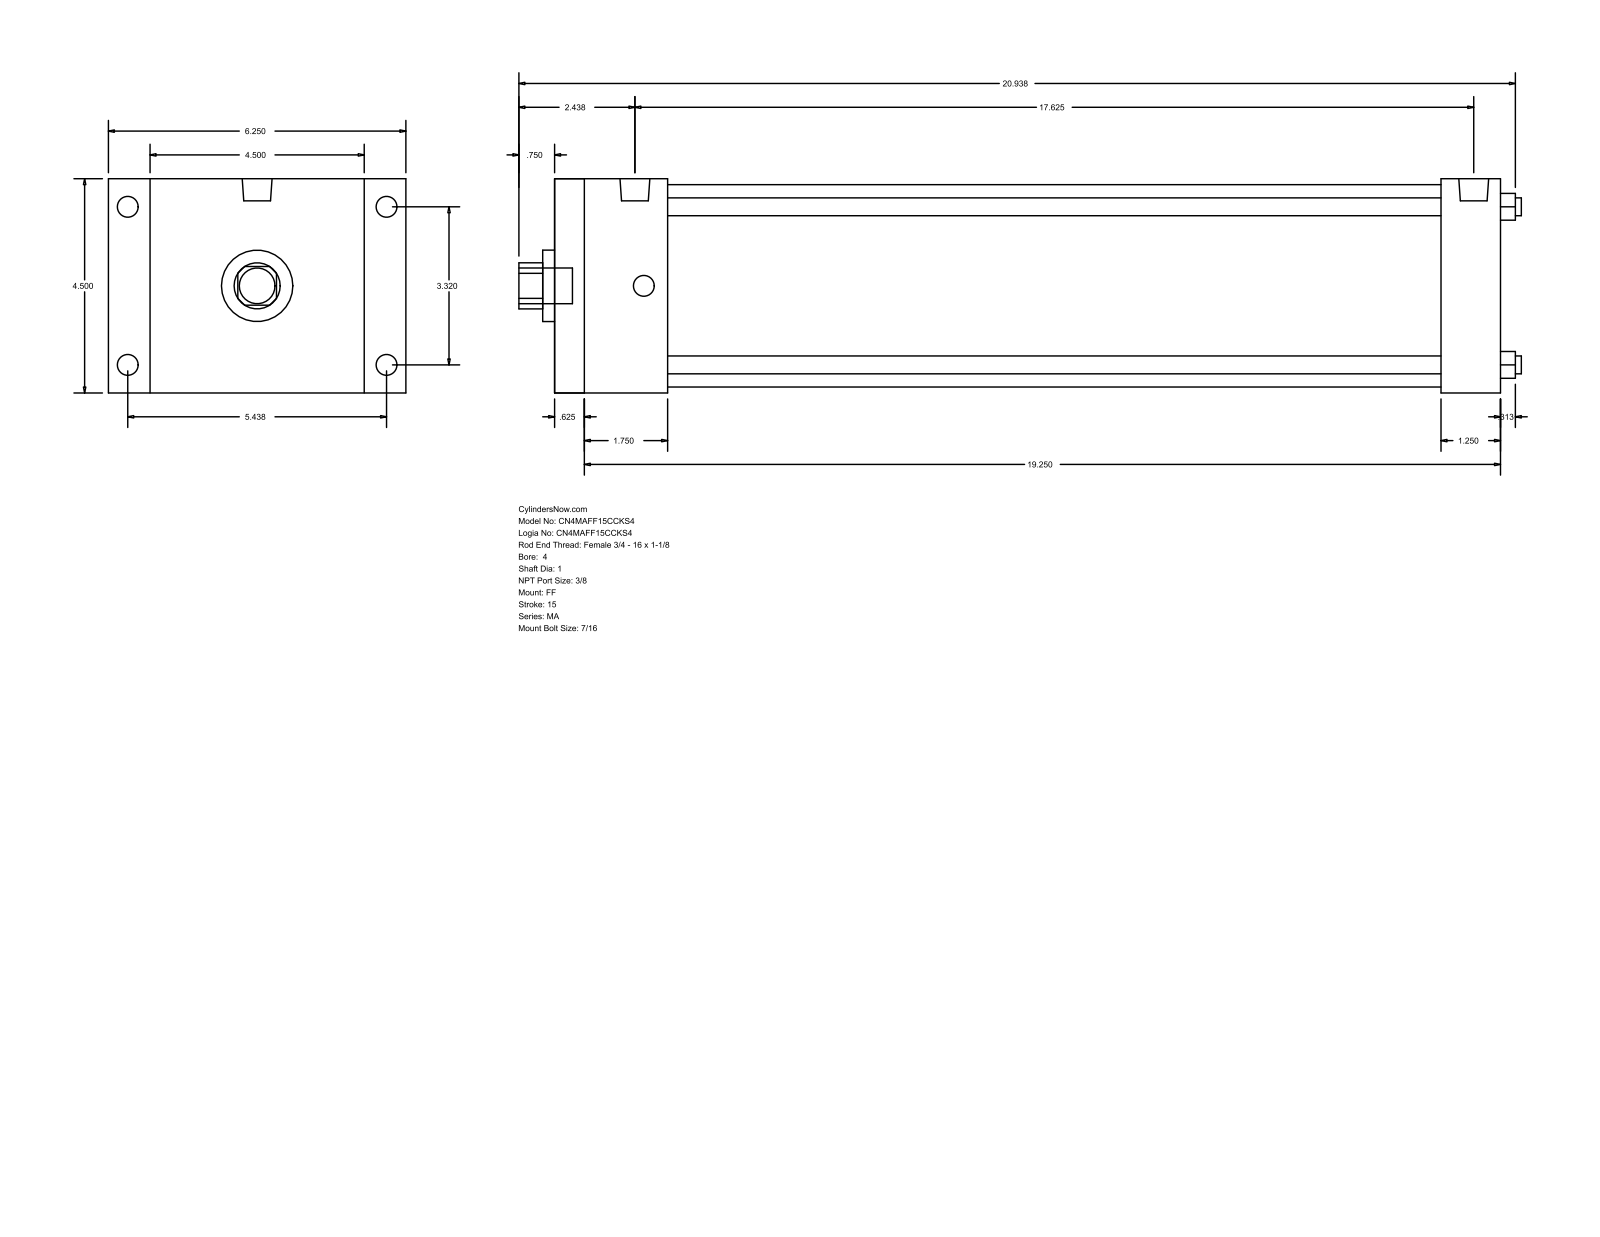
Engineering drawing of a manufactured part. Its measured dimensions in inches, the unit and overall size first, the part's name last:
Units: inches
Overall size (bounding box): 21.063 × 6.25 × 4.5
Round holes (diameter × count): ⌀0.375 ×4, ⌀1 ×1, ⌀1.5 ×1, ⌀4.25 ×1
Round bosses / shafts (diameter × count): ⌀0.437 ×8, ⌀0.627 ×2, ⌀0.75 ×1
Partial cylindrical surfaces — rounded edges, fillets, slot ends (radius × count): R0.484 ×1
Main face-to-face distances: 4.5, 19.875, 0.625, 19.25, 0.875, 5.375, 18.625, 18, 1.25, 2.375
Hole centre spacings: 2.347, 3.32, 4.695
Bodies: 0 solids, 92 faces (64 planar, 28 cylindrical, 0 other)
Part name (STEP PRODUCT): MA_FF__0400_1
STEP written by: GSSL Pune (CONFIG_CONTROL_DESIGN)
